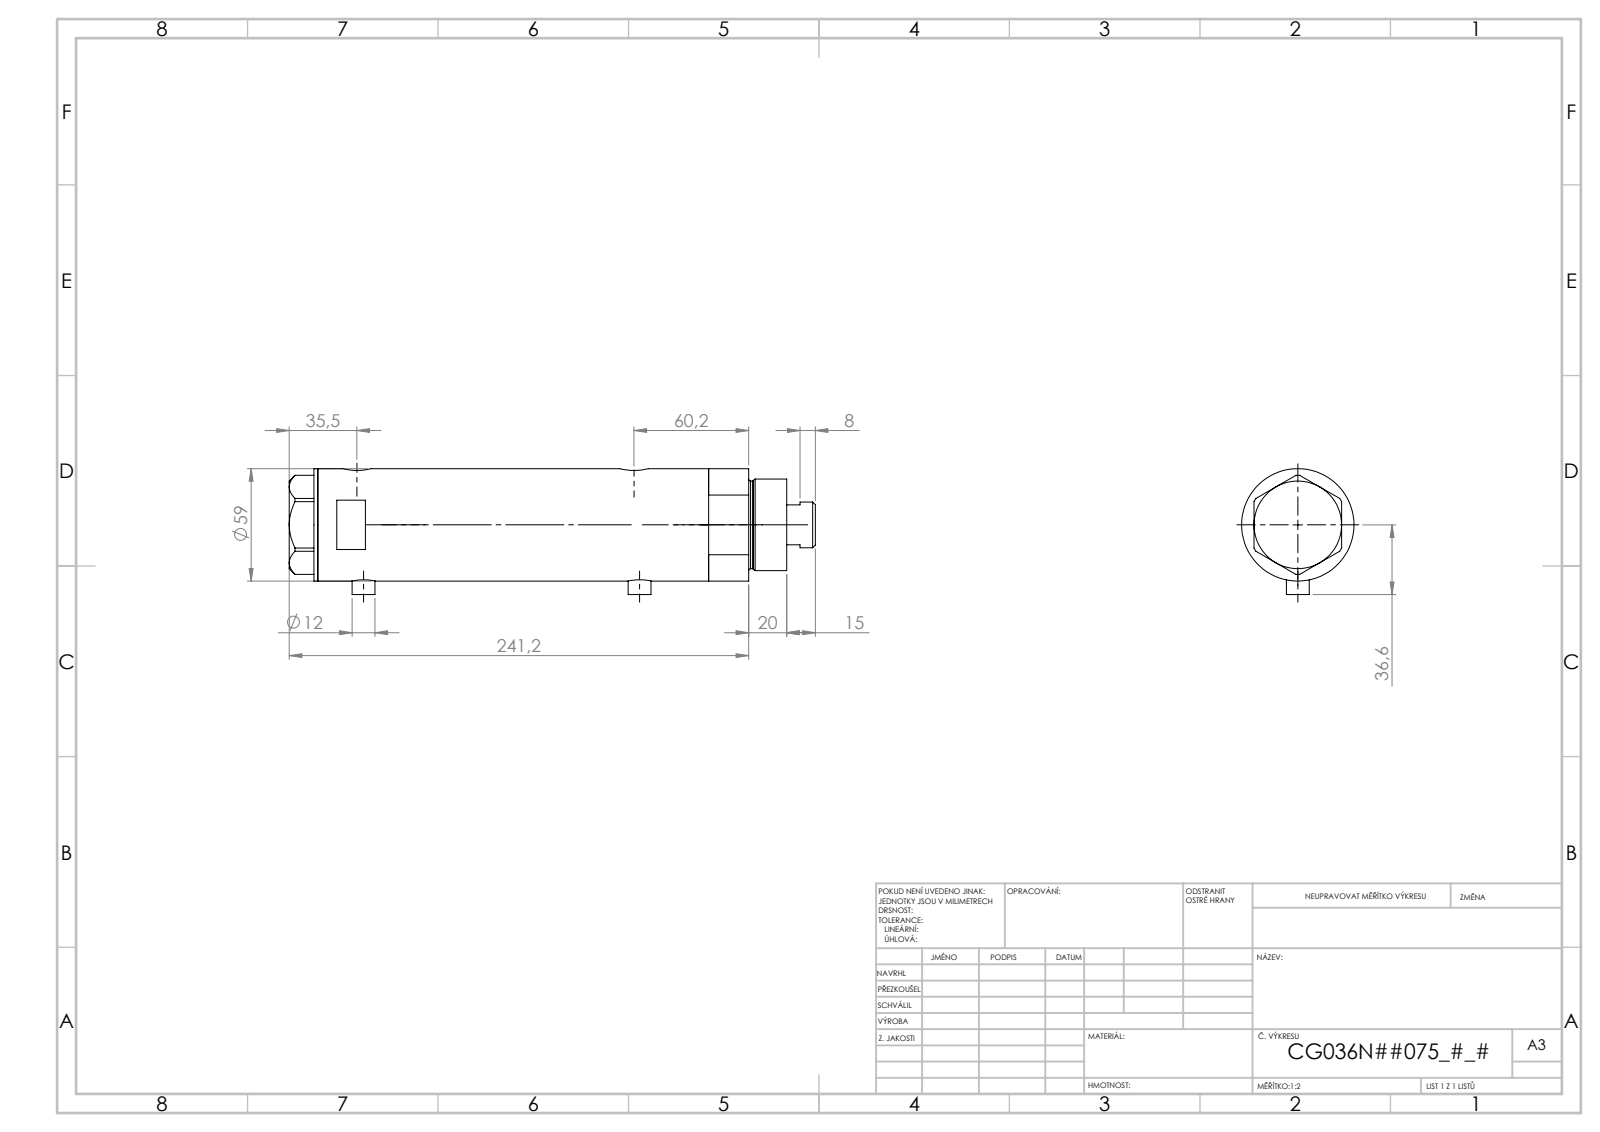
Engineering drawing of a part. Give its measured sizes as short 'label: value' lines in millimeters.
name: V270CG_MIDDLE; V270CG_VC; V270CG_BACK; V270CG_FRONT
written by: SolidWorks 2019 (CONFIG_CONTROL_DESIGN)
unit: mm
bodies: 4 solids, 126 faces (53 planar, 53 cylindrical, 20 other)
size: 238.42 × 60.1 × 59
volume: 536 664 mm³; area: 110 167 mm²
holes: 2× ⌀5, 2× ⌀9.73, 2× ⌀12.5, 2× ⌀15, 1× ⌀8.5, 1× ⌀25, 1× ⌀26.5, 1× ⌀36, 1× ⌀40, 1× ⌀52
bosses: 2× ⌀12, 1× ⌀59, 1× ⌀48, 1× ⌀46, 1× ⌀24
face distances: 23.5, 15, 38.5, 147.34, 132.34, 108.84, 223.42, 208.42, 184.92, 76.08
hole spacings: 2.9, 3.5, 107.15, 110.05, 110.65, 113.55, 2.89, 2.91
